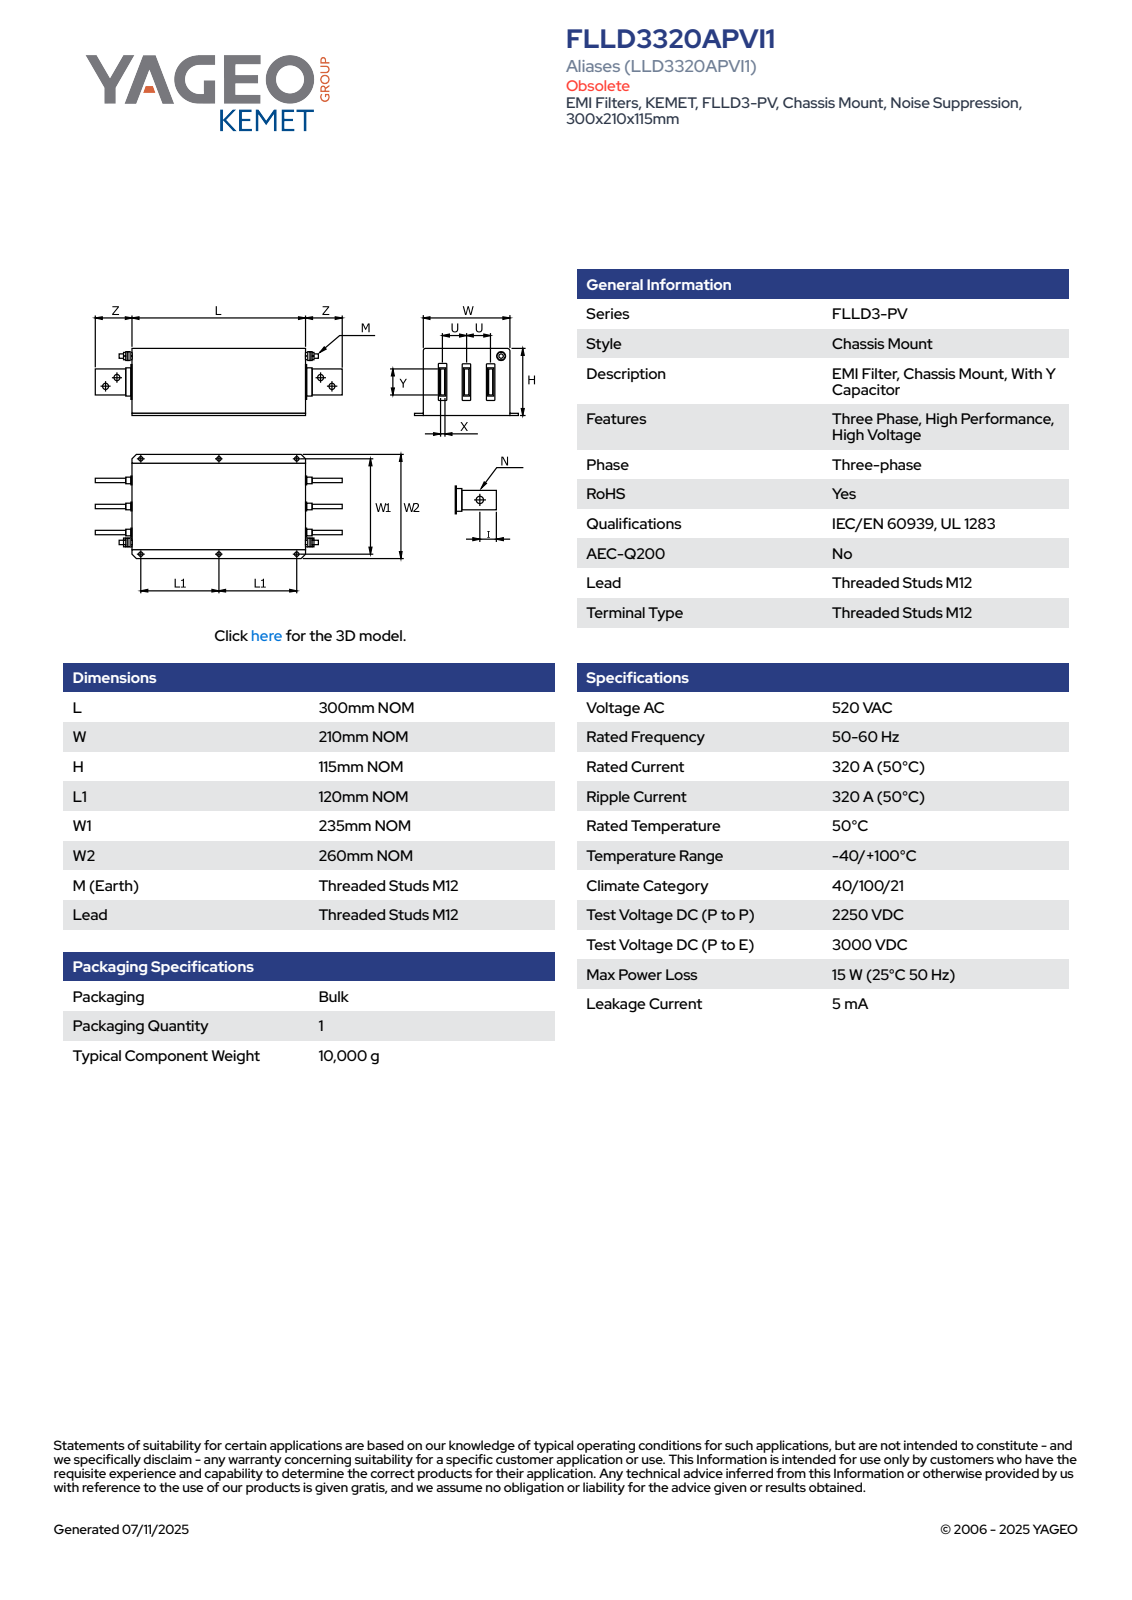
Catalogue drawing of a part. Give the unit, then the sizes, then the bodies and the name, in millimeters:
Units: millimetres
Overall size (bounding box): 390 × 260 × 115
Round holes (diameter × count): ⌀1.8 ×19, ⌀3.4 ×15, ⌀3.2 ×10, ⌀12 ×6, ⌀5 ×4, ⌀5.2 ×4, ⌀10.5 ×2, ⌀13 ×1, ⌀14 ×1
Round bosses / shafts (diameter × count): ⌀3.2 ×13, ⌀7 ×4, ⌀24 ×1, ⌀12 ×1
Partial cylindrical surfaces — rounded edges, fillets, slot ends (radius × count): R2 ×84, R0.5 ×64, R0.2 ×36, R1 ×30, R0.25 ×24, R2.5 ×10, R1.5 ×4, R3 ×2
Main face-to-face distances: 2, 1, 113, 208, 114, 298, 115, 112, 296, 206
Hole centre spacings: 120, 75, 21.47, 60, 70, 74.67, 81.39, 94.09
Volume: 594 695 mm³ · Surface area: 661 393 mm²
Bodies: 84 solids, 3106 faces (770 planar, 974 cylindrical, 1362 other)
Part name (STEP PRODUCT): 091-00223 Busbar insulation 6x25 RevD; 094-00224 Case 320-400A 300x210x115 RevC; Busbar 6x25^FLLD3400APVI1_EXT; Tank bush M4 (+8 more)
STEP written by: SolidWorks 2021 (AUTOMOTIVE_DESIGN)
